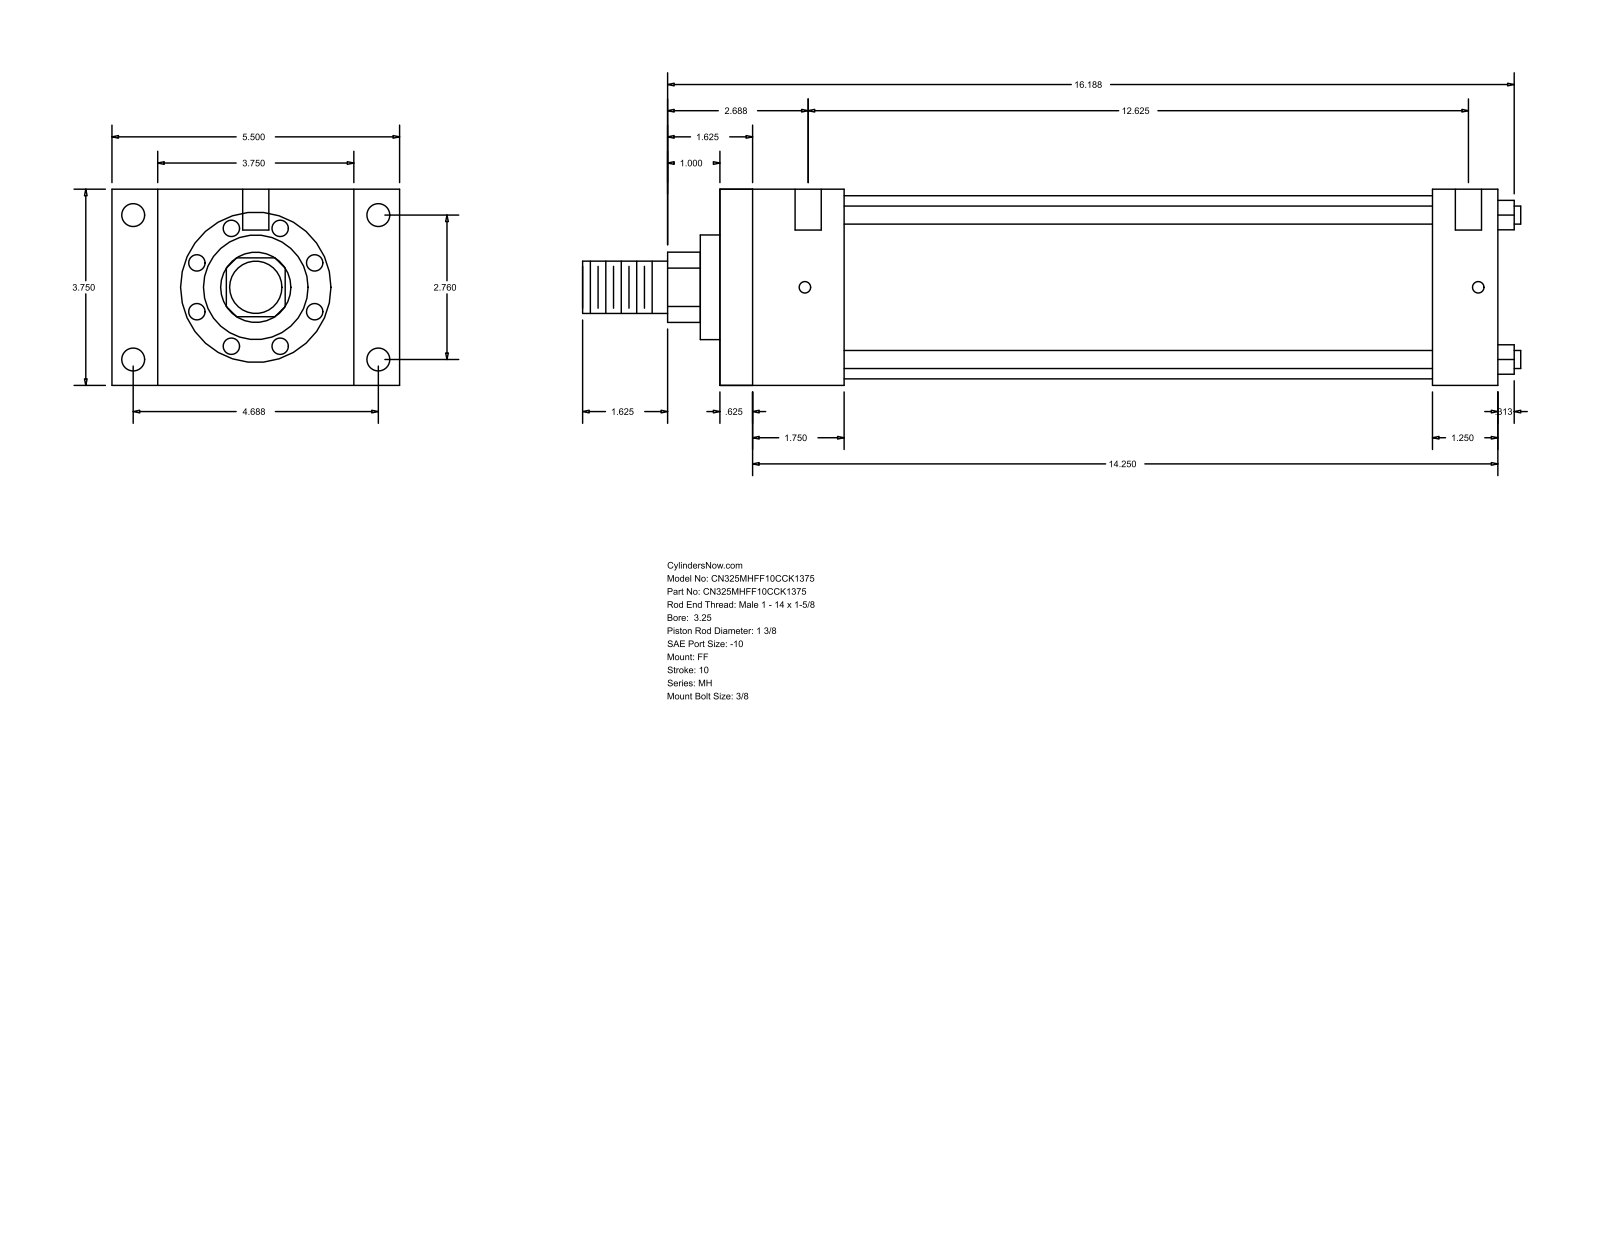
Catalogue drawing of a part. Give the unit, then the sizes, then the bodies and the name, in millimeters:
Units: millimetres
Overall size (bounding box): 455.61 × 139.7 × 95.25
Round holes (diameter × count): ⌀5.56 ×4, ⌀11.13 ×4, ⌀12.7 ×2
Round bosses / shafts (diameter × count): ⌀8.76 ×4, ⌀88.9 ×1, ⌀50.8 ×1, ⌀34.92 ×1, ⌀25.4 ×1
Partial cylindrical surfaces — rounded edges, fillets, slot ends (radius × count): R17.06 ×1
Main face-to-face distances: 95.24, 377.83, 15.87, 361.96, 22.23, 117.47, 346.08, 330.21, 31.75, 60.32
Hole centre spacings: 70.1, 119.06, 138.16, 327.03, 1.59, 4.76, 320.68, 322.27
Bodies: 0 solids, 92 faces (64 planar, 28 cylindrical, 0 other)
Part name (STEP PRODUCT): MH_FF__0325_1.375
STEP written by: GSSL Pune (CONFIG_CONTROL_DESIGN)
